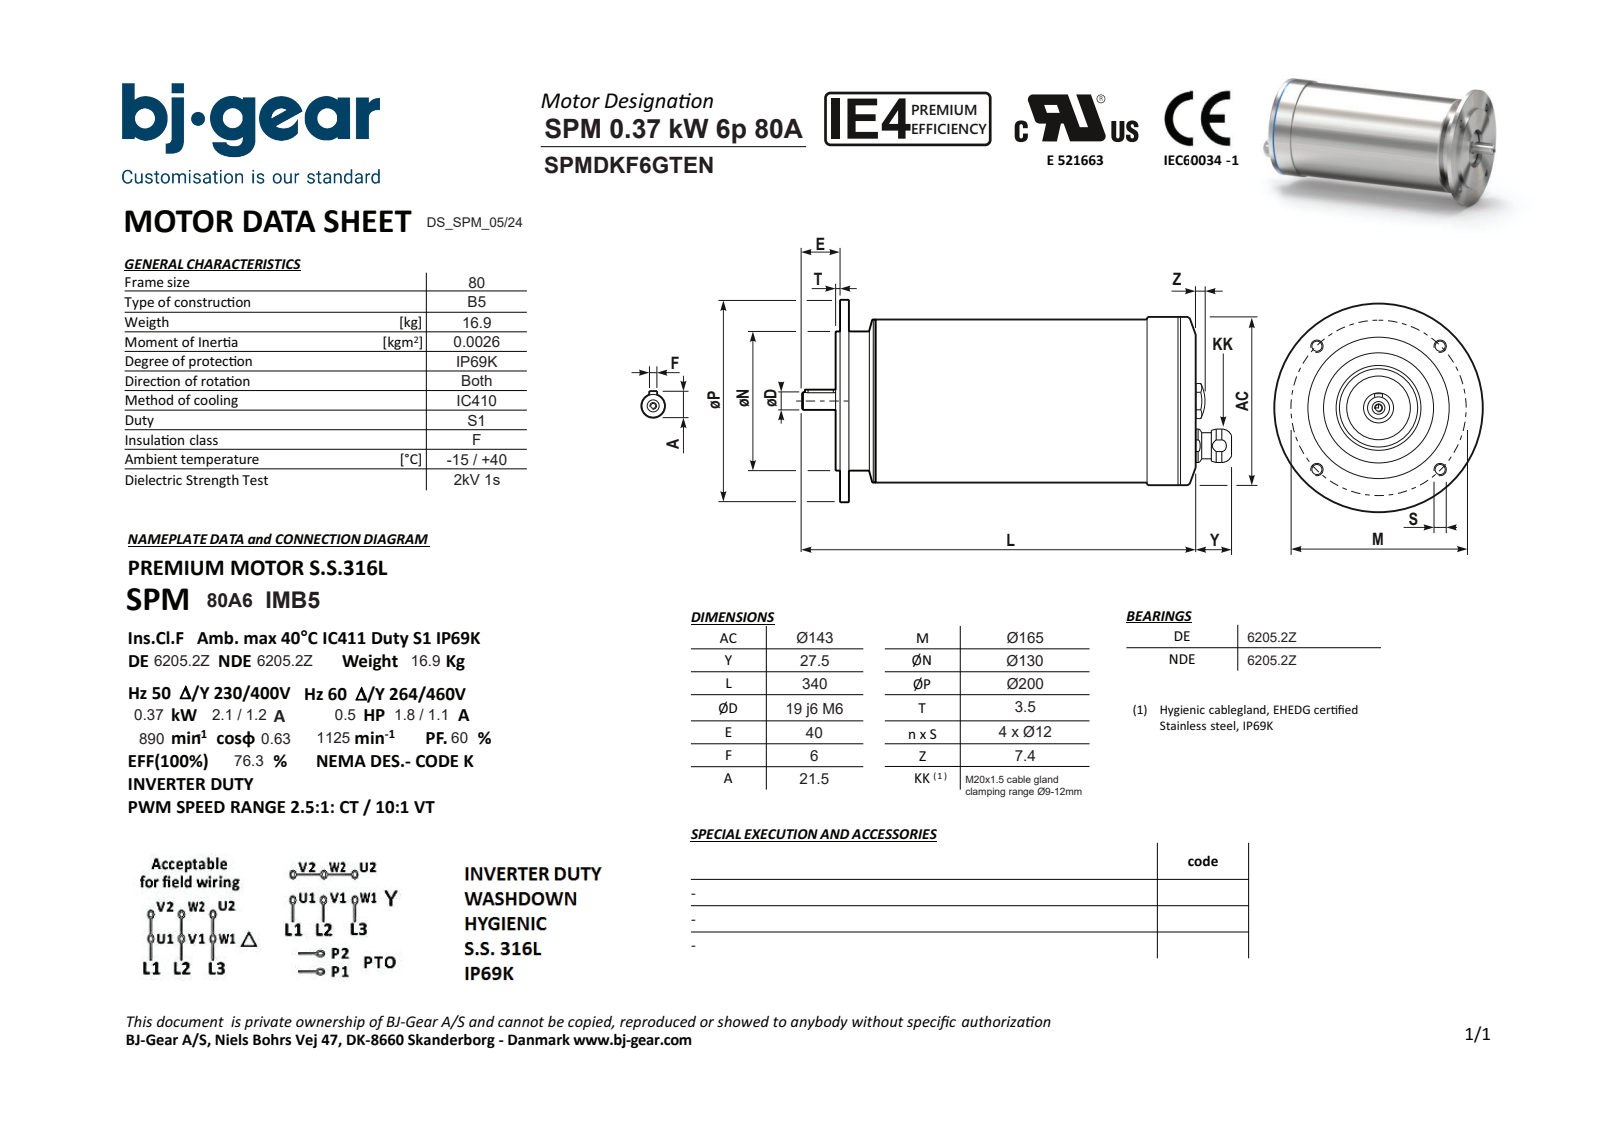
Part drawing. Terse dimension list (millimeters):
name: SPMDKF6GTENN4KSA1-N---NNN
written by: Solid Edge (AUTOMOTIVE_DESIGN)
unit: mm
bodies: 1 solid, 79 faces (30 planar, 28 cylindrical, 21 other)
size: 367.5 × 200 × 200
volume: 4 736 000 mm³; area: 203 697 mm²
holes: 4× ⌀12, 1× ⌀4.92, 1× ⌀6.4, 1× ⌀7, 1× ⌀13.4, 1× ⌀68
bosses: 1× ⌀200, 1× ⌀143, 1× ⌀142.98, 1× ⌀139, 1× ⌀138.98, 1× ⌀130, 1× ⌀25, 1× ⌀20
rounds: 2× R3, 1× R12.8
face distances: 8, 11.5, 3.5, 292, 300, 303.5, 6, 2, 294, 9.5
hole spacings: 82.51, 116.68, 61.78, 112.63, 165.01, 38
